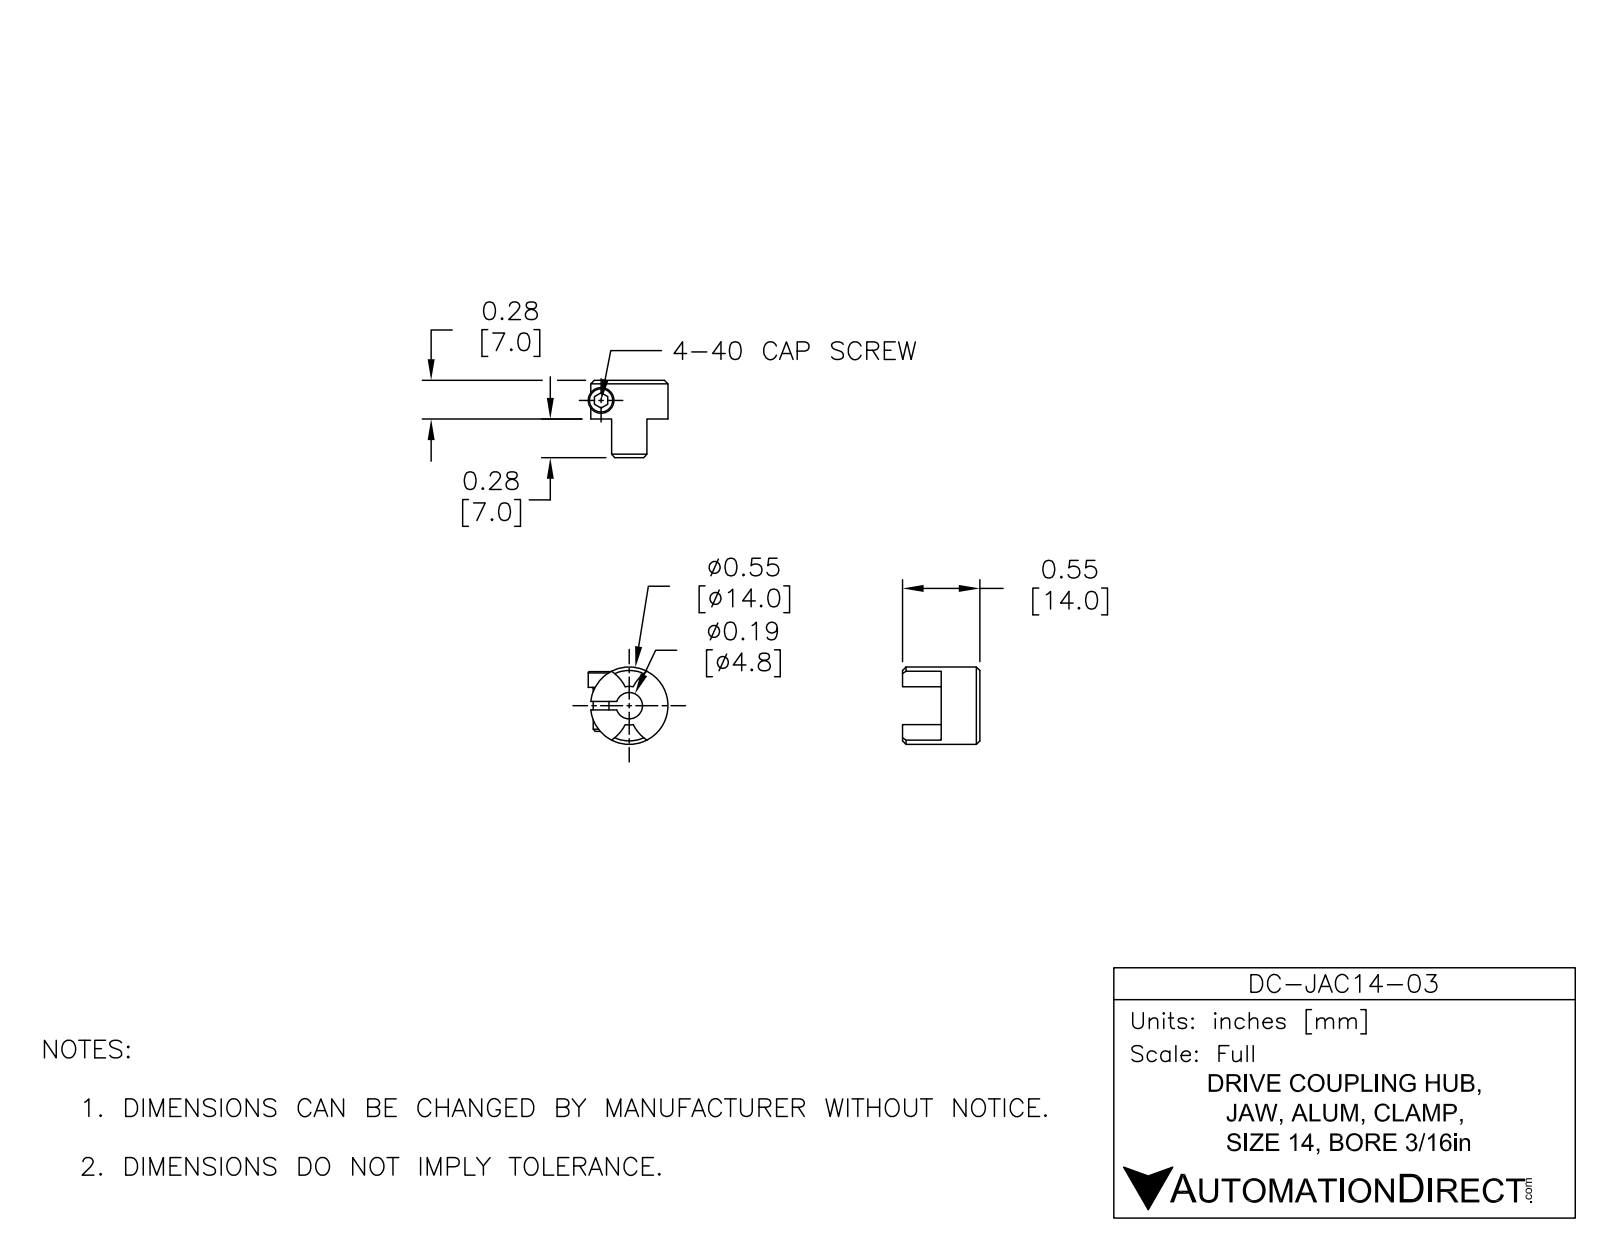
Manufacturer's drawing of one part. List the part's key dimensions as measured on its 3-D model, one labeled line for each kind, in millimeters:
Part name (STEP PRODUCT): DC-JAC14-03
STEP written by: SolidWorks 2015 (AUTOMOTIVE_DESIGN)
Units: millimetres
Bodies: 1 solid, 30 faces (7 planar, 17 cylindrical, 6 other)
Overall size (bounding box): 13.97 × 13.97 × 13.93
Volume: 989 mm³ · Surface area: 944 mm²
Round holes (diameter × count): ⌀3.28 ×1, ⌀4.76 ×1
Round bosses / shafts (diameter × count): ⌀13.97 ×1
Partial cylindrical surfaces — rounded edges, fillets, slot ends (radius × count): R7.52 ×2, R2.39 ×1, R3.49 ×1
Main face-to-face distances: 6.99, 1.52, 13.97, 6.98, 2.54, 4.06
